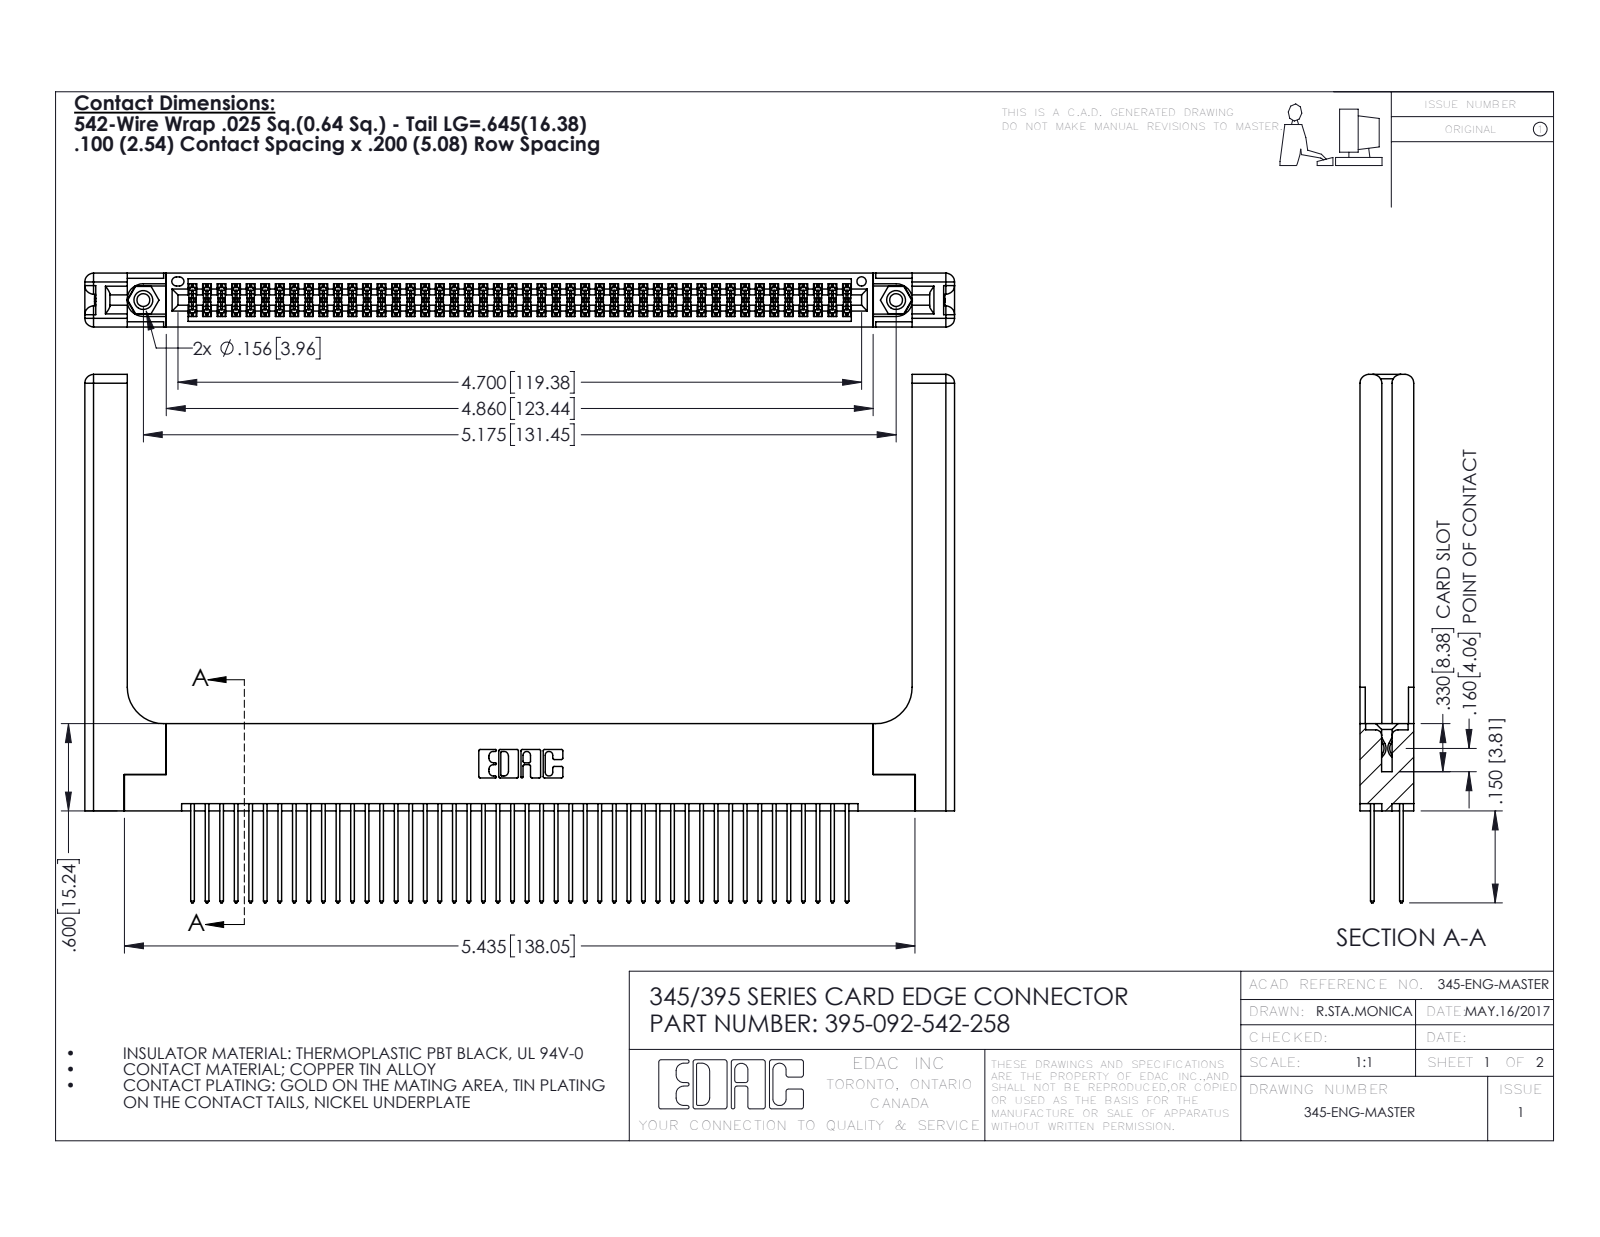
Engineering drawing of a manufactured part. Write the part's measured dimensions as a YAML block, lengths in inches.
part_name: "395-092-542-258; 345 Part_Flush Mounting Lugs - 0.156 Dia-TH; 345-292-001_345-293-142; 345-220-058_345-220-058 (+1 more)"
step_written_by: "SolidWorks 2016 (CONFIG_CONTROL_DESIGN)"
units: inches
bodies: {solids: 97, faces: 4982, planar: 3264, cylindrical: 1658, other: 60}
overall_size: [5.979, 3.632, 0.37]
volume: 1.446
surface_area: 45.94
round_holes:
  - {diameter: 0.089, count: 2}
  - {diameter: 0.125, count: 2}
  - {diameter: 0.156, count: 2}
  - {diameter: 0.064, count: 1}
round_bosses_or_shafts:
  - {diameter: 0.155, count: 2}
partial_cylinders:
  - {radius: 0.006, count: 138}
  - {radius: 0.01, count: 92}
  - {radius: 0.01, count: 22}
  - {radius: 0.06, count: 16}
  - {radius: 0.007, count: 6}
  - {radius: 0.031, count: 6}
  - {radius: 0.026, count: 3}
  - {radius: 0.014, count: 2}
face_to_face_distances: [0.072, 0.298, 0.37, 0.2, 0.098, 0.272, 0.025, 0.225, 0.175, 0.148]
hole_center_spacings: [0.27, 4.939, 5.175]
